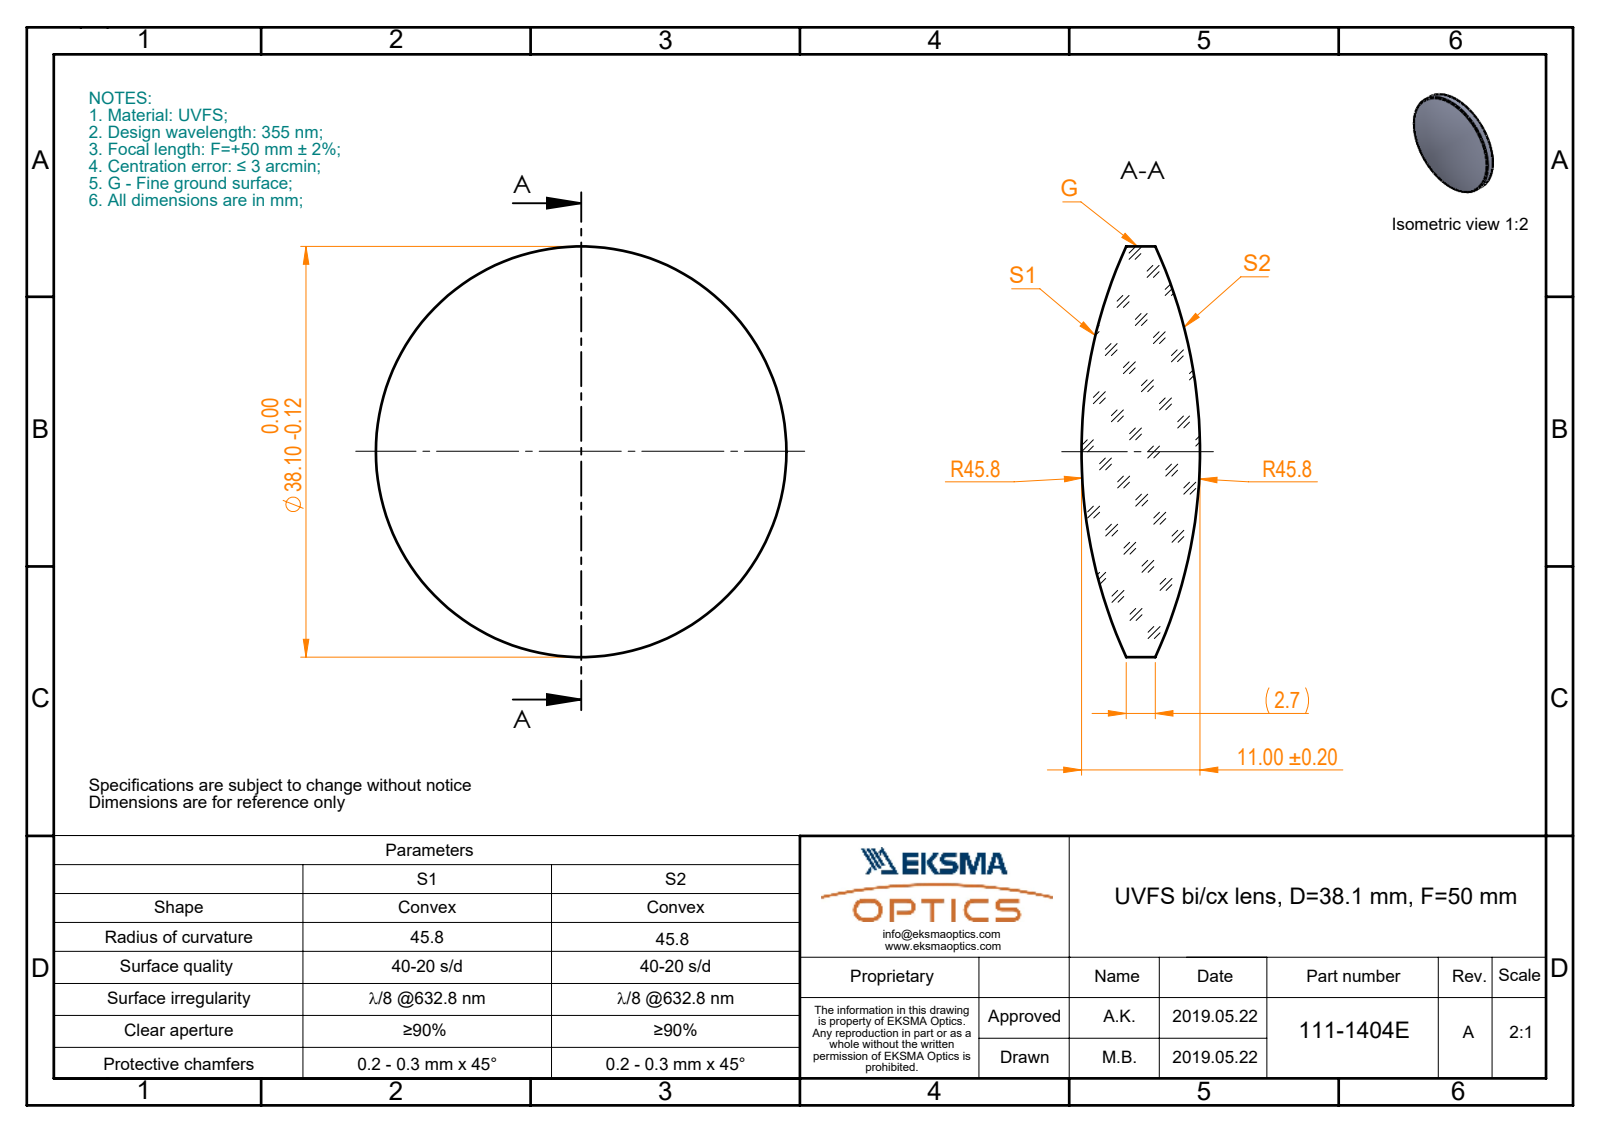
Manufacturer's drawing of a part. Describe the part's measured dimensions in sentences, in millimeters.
The part is named "111-1404E UVFS bi-cx 38.1 F50". Its 3-D file was written by "SolidWorks 2017 (CONFIG_CONTROL_DESIGN)". It is 1 solid with 6 faces: 0 planar, 2 cylindrical and 4 other. Overall it measures 38.1 by 38.1 by 11 millimeters. Its volume is 7 880 cubic millimeters and its surface area 2 711 square millimeters. Round bosses or shafts: 1 of diameter 38.1.
